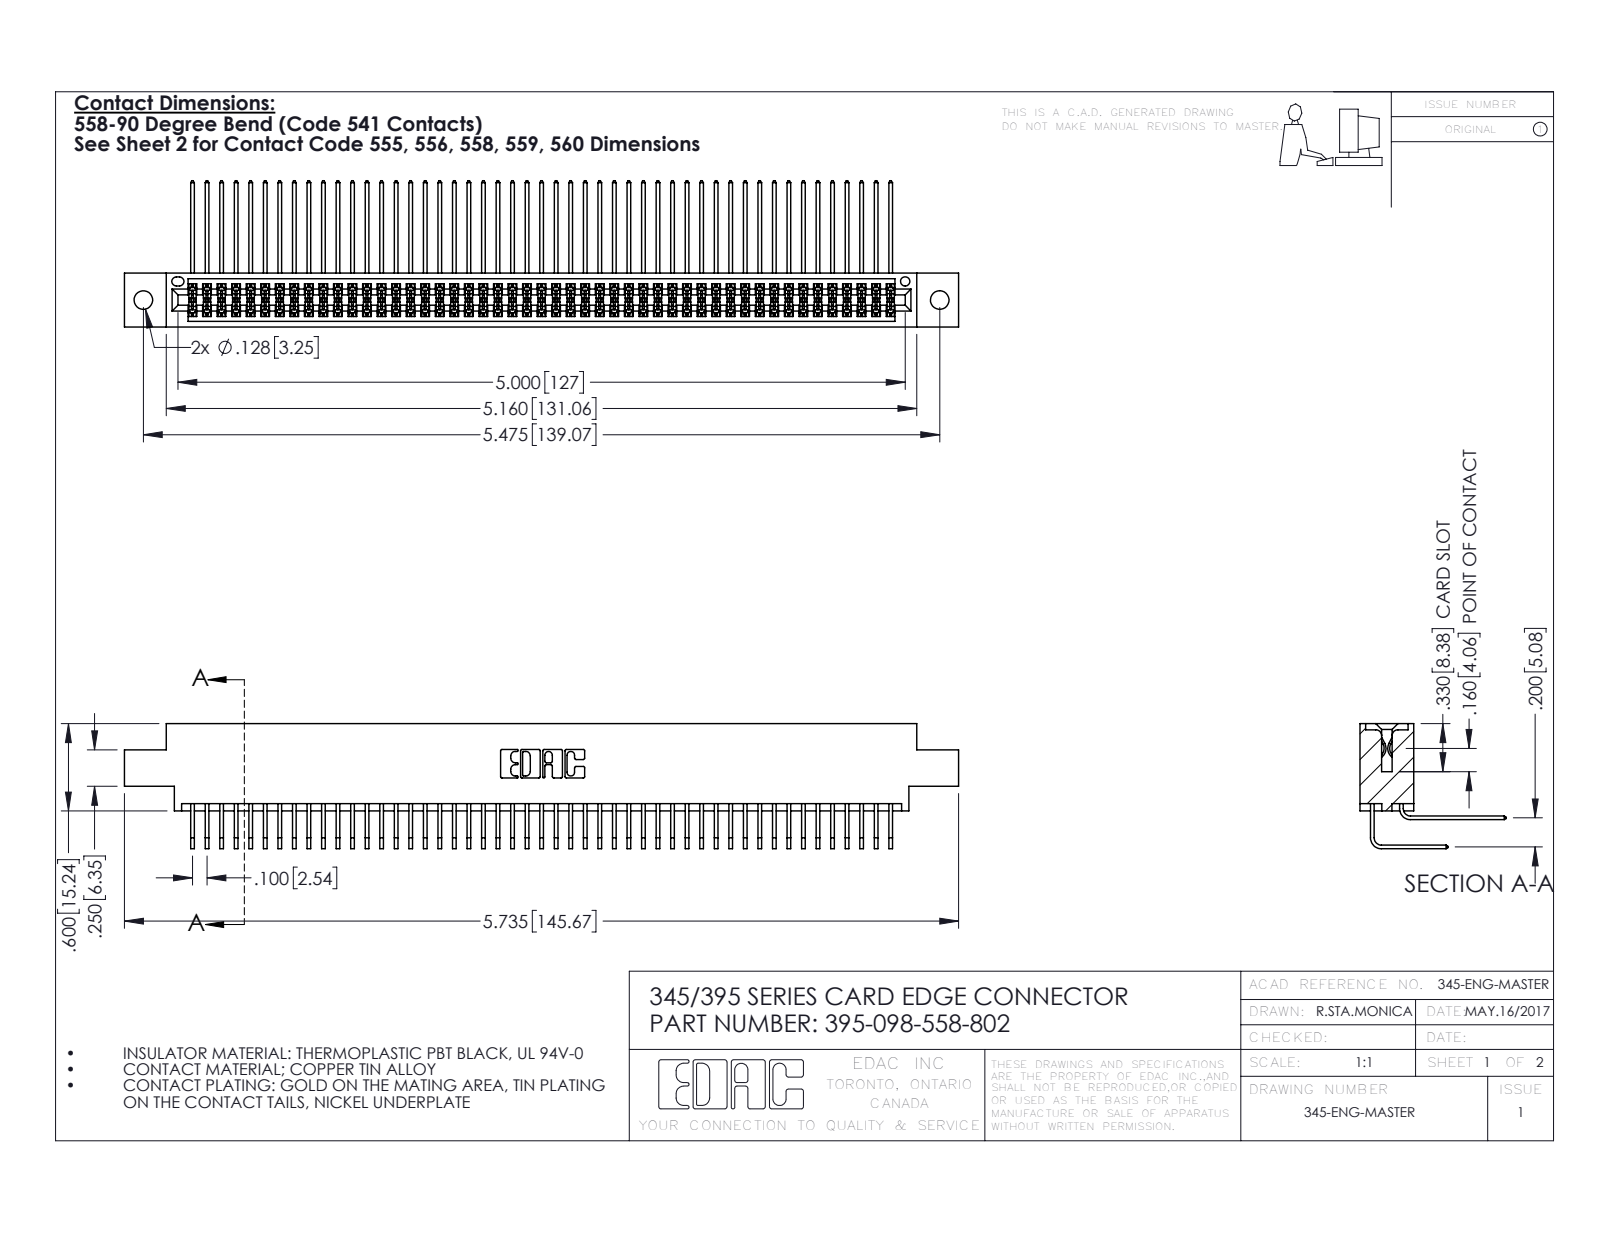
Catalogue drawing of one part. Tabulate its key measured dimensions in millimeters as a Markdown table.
| quantity | value |
| --- | --- |
| part name | 345-292-001_558 Tail - 2; 345-292-001_558 559 Tail - 1; 345 Part_0.170 Offset - 0.128 Dia; 395-098-558-802 |
| STEP written by | SolidWorks 2016 (CONFIG_CONTROL_DESIGN) |
| units | millimeters |
| bodies | 99 solids, 5226 faces (3514 planar, 1712 cylindrical, 0 other) |
| overall size | 145.7 × 25.5 × 21.8 |
| volume | 14 600 mm³ |
| surface area | 24 290 mm² |
| round holes (diameter × count) | 3.3 × 2, 1.6 × 1 |
| partial cylindrical surfaces (radius × count) | 0.2 × 148, 0.3 × 22, 0.2 × 6, 0.8 × 6, 0.7 × 3, 0.4 × 2, 0.5 × 2, 0.6 × 2 |
| main face-to-face distances | 1.8, 7.6, 5.1, 9.4, 2.5, 6.9, 0.6, 5.7, 4.4, 0.6 |
| hole center spacings | 6.9, 133.1, 139.1 |
